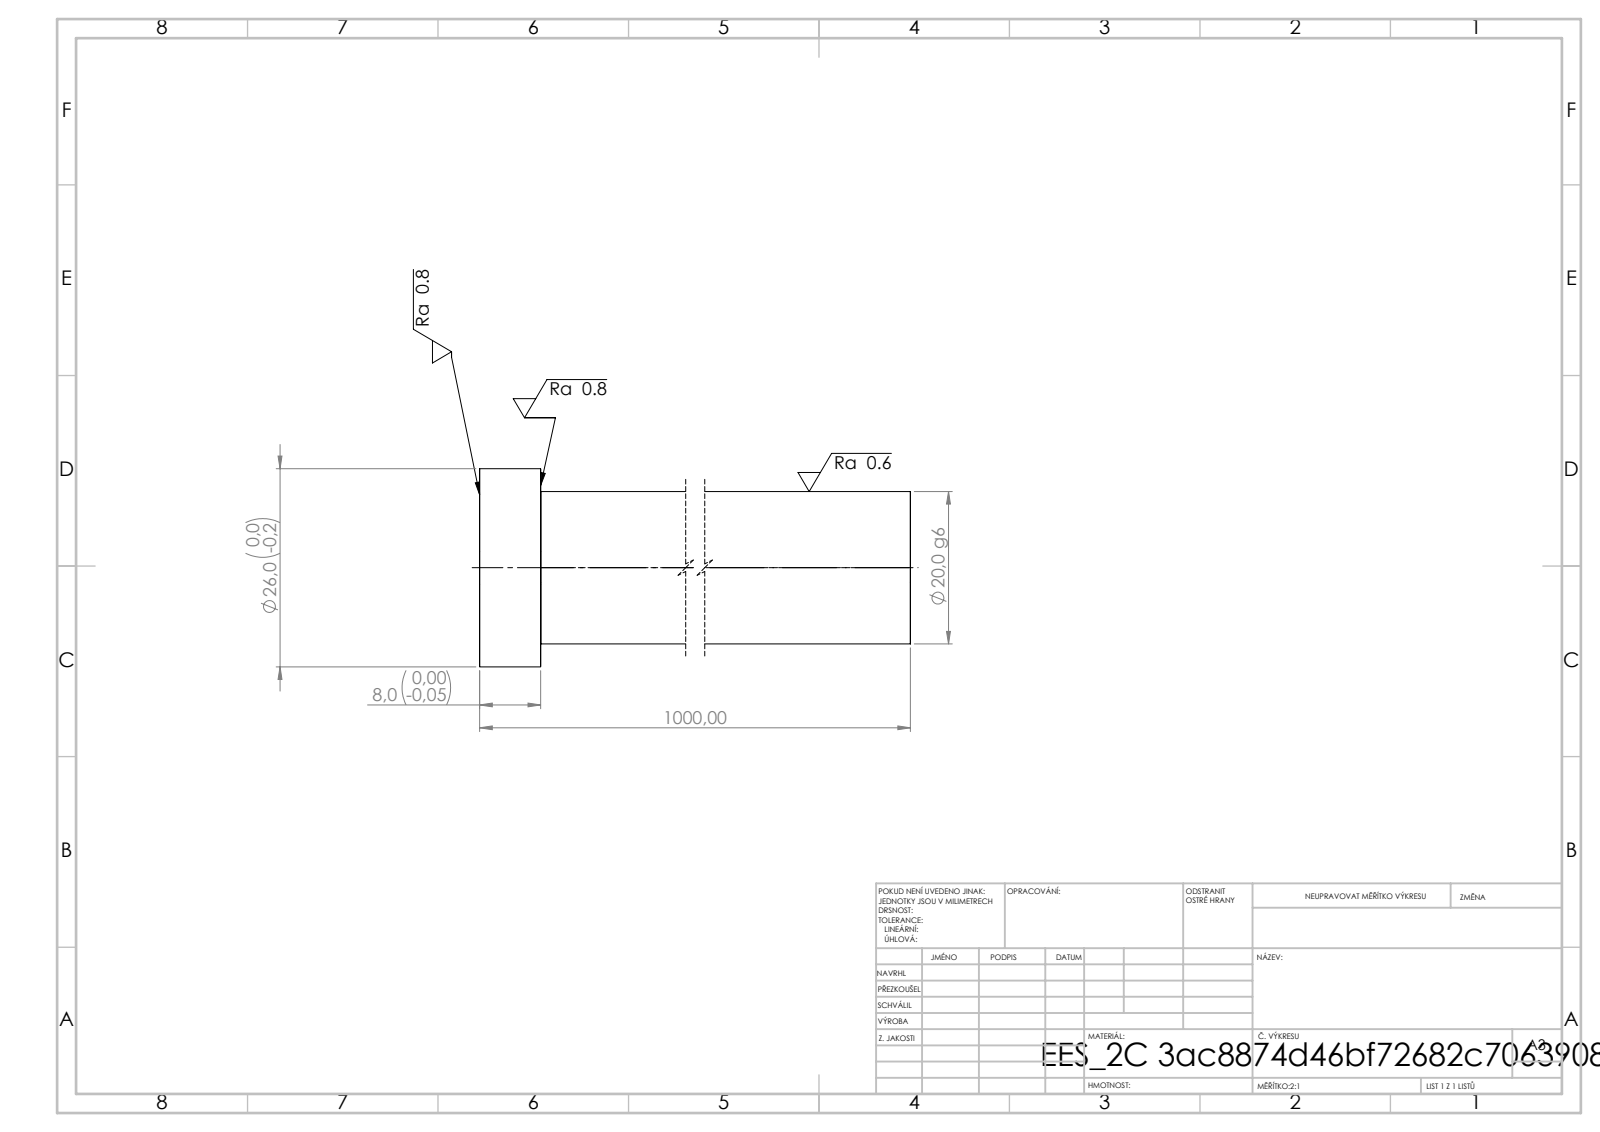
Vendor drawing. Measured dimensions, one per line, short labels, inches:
written by: SolidWorks 2019 (CONFIG_CONTROL_DESIGN)
unit: in
bodies: 1 solid, 7 faces (3 planar, 4 cylindrical, 0 other)
size: 39.37 × 1.024 × 1.024
volume: 19.28 in³; area: 99.27 in²
bosses: 1× ⌀1.024, 1× ⌀0.787
face distances: 39.37, 0.315, 39.055
